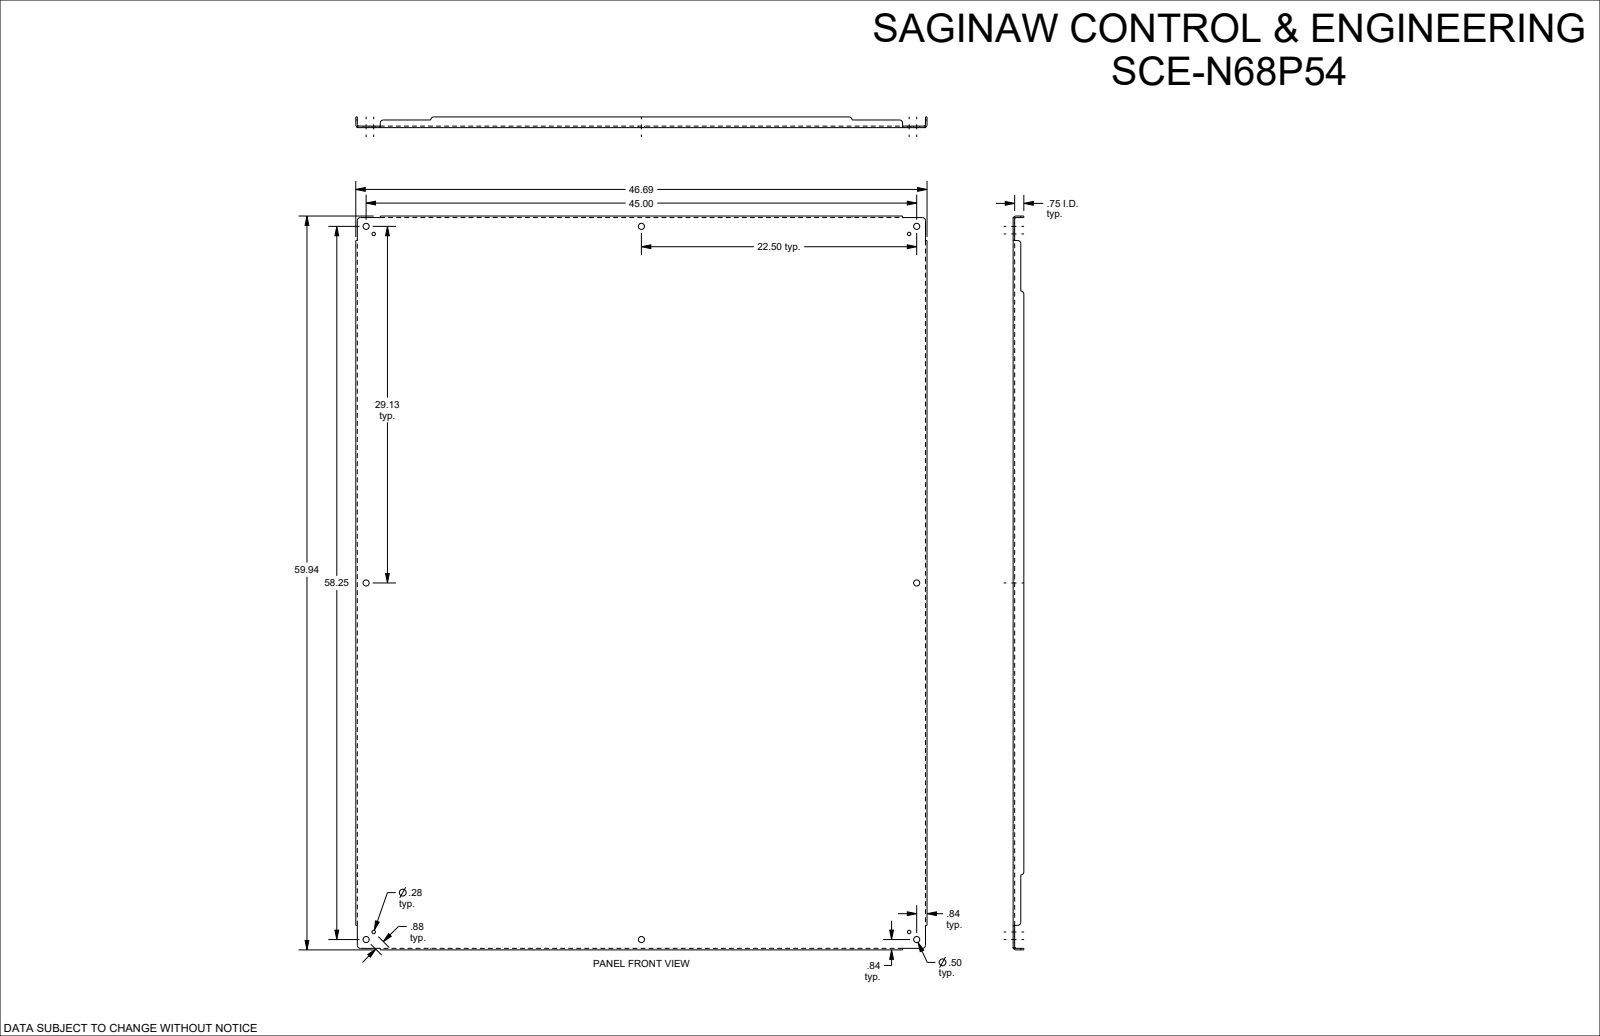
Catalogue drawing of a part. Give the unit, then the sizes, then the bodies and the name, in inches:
Units: inches
Overall size (bounding box): 59.938 × 46.688 × 0.875
Round holes (diameter × count): ⌀0.5 ×8, ⌀0.281 ×4
Partial cylindrical surfaces — rounded edges, fillets, slot ends (radius × count): R0.25 ×12, R0.112 ×4, R0.237 ×4
Main face-to-face distances: 0.125, 46.563, 0.125, 59.813, 46.438, 46.687, 59.687, 59.938, 0.75, 0.875
Hole centre spacings: 0.875, 21.89, 22.5, 28.513, 29.125, 36.804, 44.385, 52.747
Volume: 364.9 in³ · Surface area: 5 868 in²
Bodies: 1 solid, 122 faces (46 planar, 52 cylindrical, 24 other)
Part name (STEP PRODUCT): SCE-N68P54
STEP written by: SolidWorks 2023 (AUTOMOTIVE_DESIGN)
